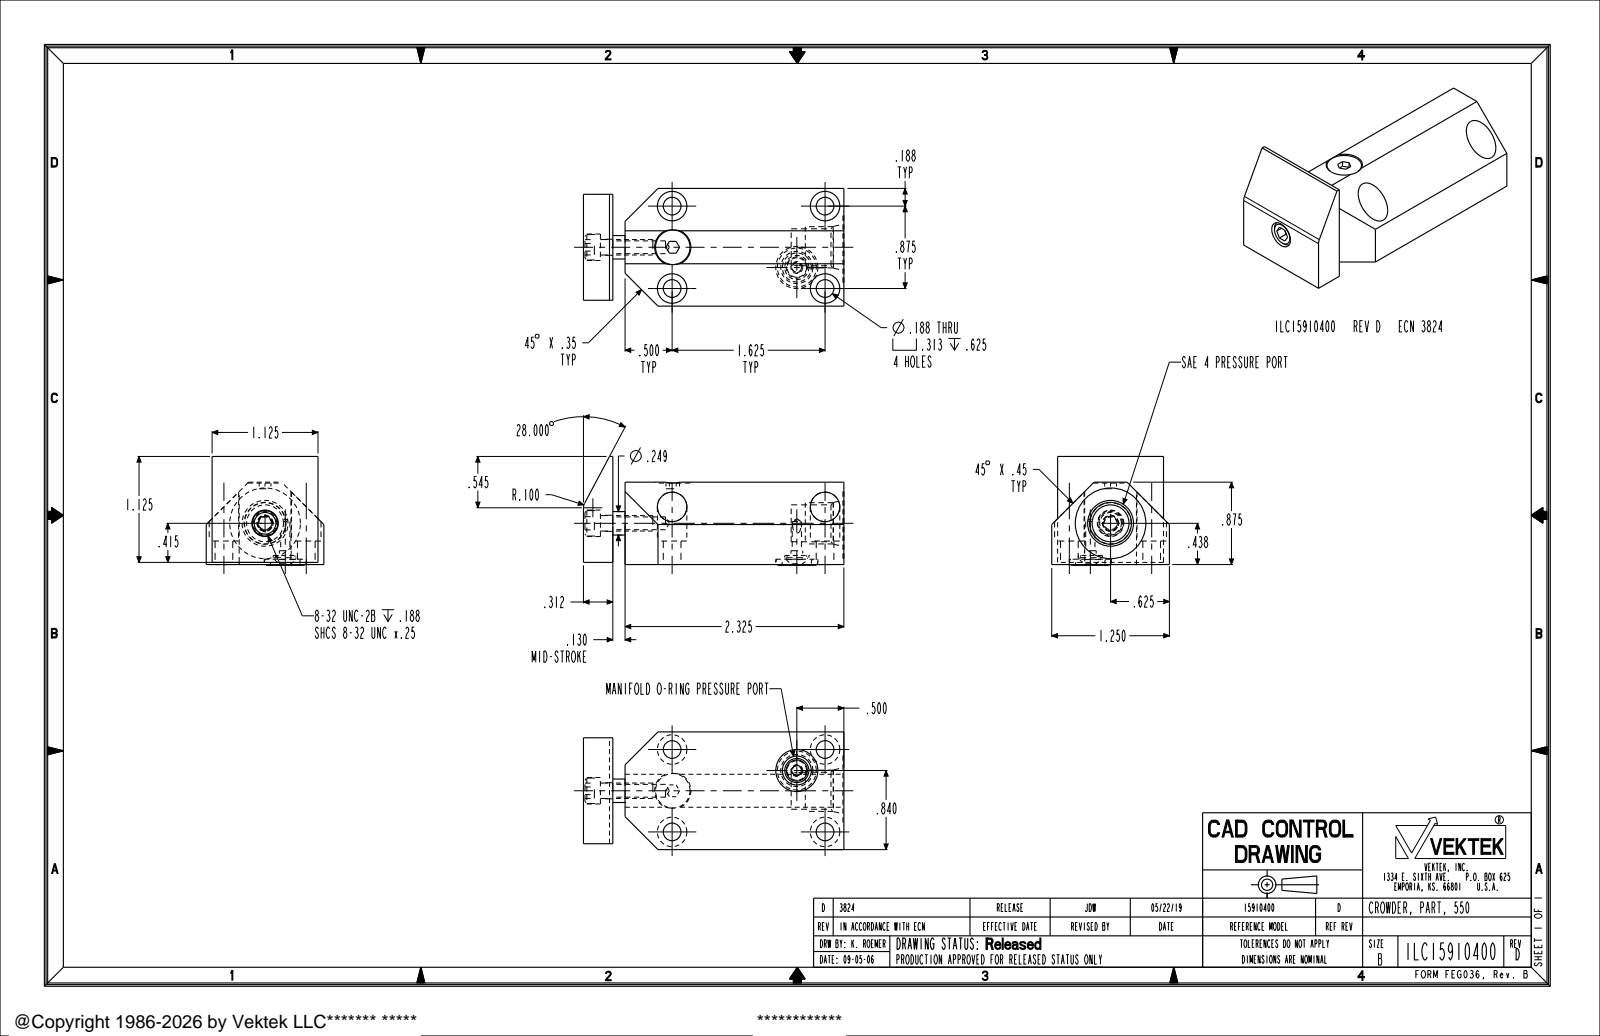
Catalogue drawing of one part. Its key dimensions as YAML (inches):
part_name: "ILC15910400"
step_written_by: "PRO/ENGINEER BY PARAMETRIC TECHNOLOGY CORPORATION, 2013320 (AUTOMOTIVE_DESIGN)"
units: inches
bodies: {solids: 1, faces: 118, planar: 53, cylindrical: 49, other: 16}
overall_size: [2.767, 1.25, 1.156]
volume: 2.09
surface_area: 17.82
round_holes:
  - {diameter: 0.188, count: 4}
  - {diameter: 0.313, count: 4}
  - {diameter: 0.098, count: 1}
  - {diameter: 0.125, count: 1}
  - {diameter: 0.136, count: 1}
  - {diameter: 0.171, count: 1}
  - {diameter: 0.256, count: 1}
  - {diameter: 0.281, count: 1}
  - {diameter: 0.392, count: 1}
  - {diameter: 0.447, count: 1}
  - {diameter: 0.75, count: 1}
round_bosses_or_shafts:
  - {diameter: 0.438, count: 1}
  - {diameter: 0.27, count: 1}
  - {diameter: 0.249, count: 1}
  - {diameter: 0.224, count: 1}
  - {diameter: 0.207, count: 1}
  - {diameter: 0.164, count: 1}
partial_cylinders:
  - {radius: 0.1, count: 1}
face_to_face_distances: [1.25, 0.875, 0.312, 0.063, 1.188, 2.455, 2.767, 2.325, 0.13, 0.442]
hole_center_spacings: [0.875, 1.625, 1.846, 0.374, 0.718, 1.343, 1.476]
